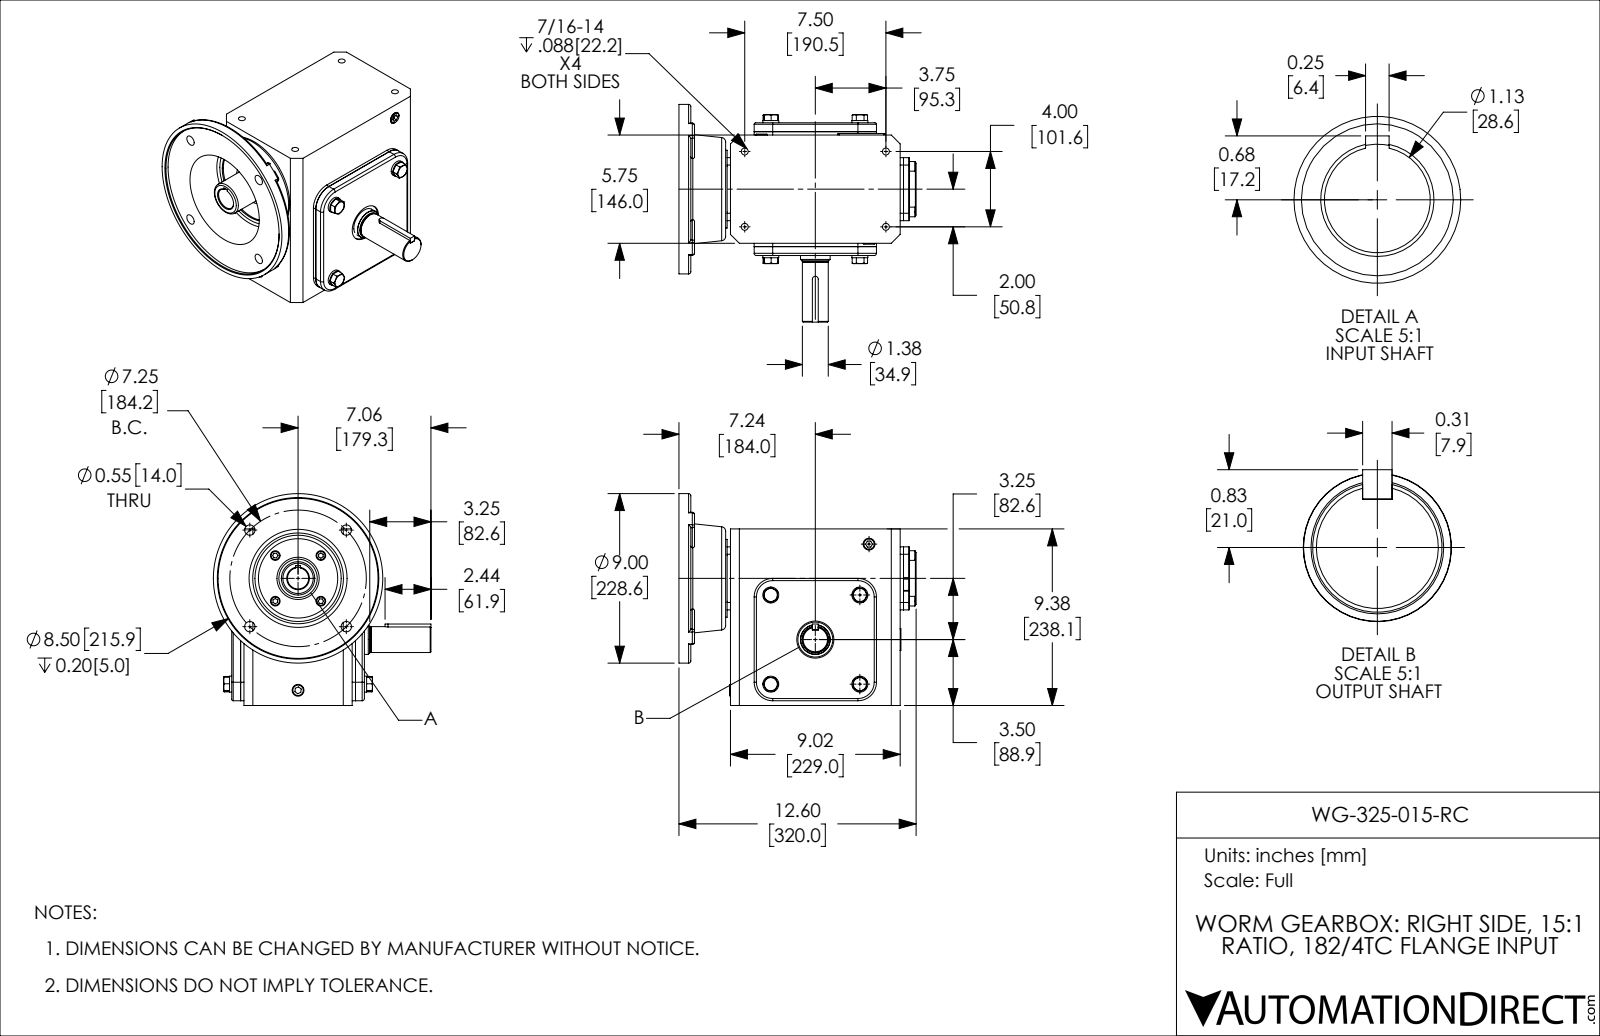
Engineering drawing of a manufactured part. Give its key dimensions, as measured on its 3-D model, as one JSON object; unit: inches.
{"part_name": "WG-325-015-RC", "step_written_by": "SolidWorks 2017 (AUTOMOTIVE_DESIGN)", "units": "inches", "bodies": {"solids": 40, "faces": 654, "planar": 336, "cylindrical": 196, "other": 122}, "overall_size": [12.598, 11.559, 11.25], "volume_in3": 529.7, "surface_area_in2": 1026, "round_holes": [[0.354, 4], [0.368, 4], [0.551, 4], [0.628, 3], [0.591, 1], [0.978, 1], [1.125, 1], [1.181, 1], [1.969, 1], [2.244, 1], [2.441, 1], [2.756, 1]], "round_bosses_or_shafts": [[0.846, 4], [0.512, 4], [9, 1], [4.134, 1], [2.835, 1], [1.772, 1], [1.575, 1], [1.375, 1]], "partial_cylinders_radius": [[0.118, 14], [0.079, 11], [0.394, 4], [0.906, 4], [0.984, 4], [0.02, 2], [0.039, 2], [0.156, 1]], "face_to_face_distances": [0.079, 0.177, 6.496, 0.394, 6.969, 0.472, 6.575, 6.398, 0.571, 0.65], "hole_center_spacings": [4.009, 1.713, 1.913, 2.422, 3.625, 5.127, 5.338, 2.372]}
